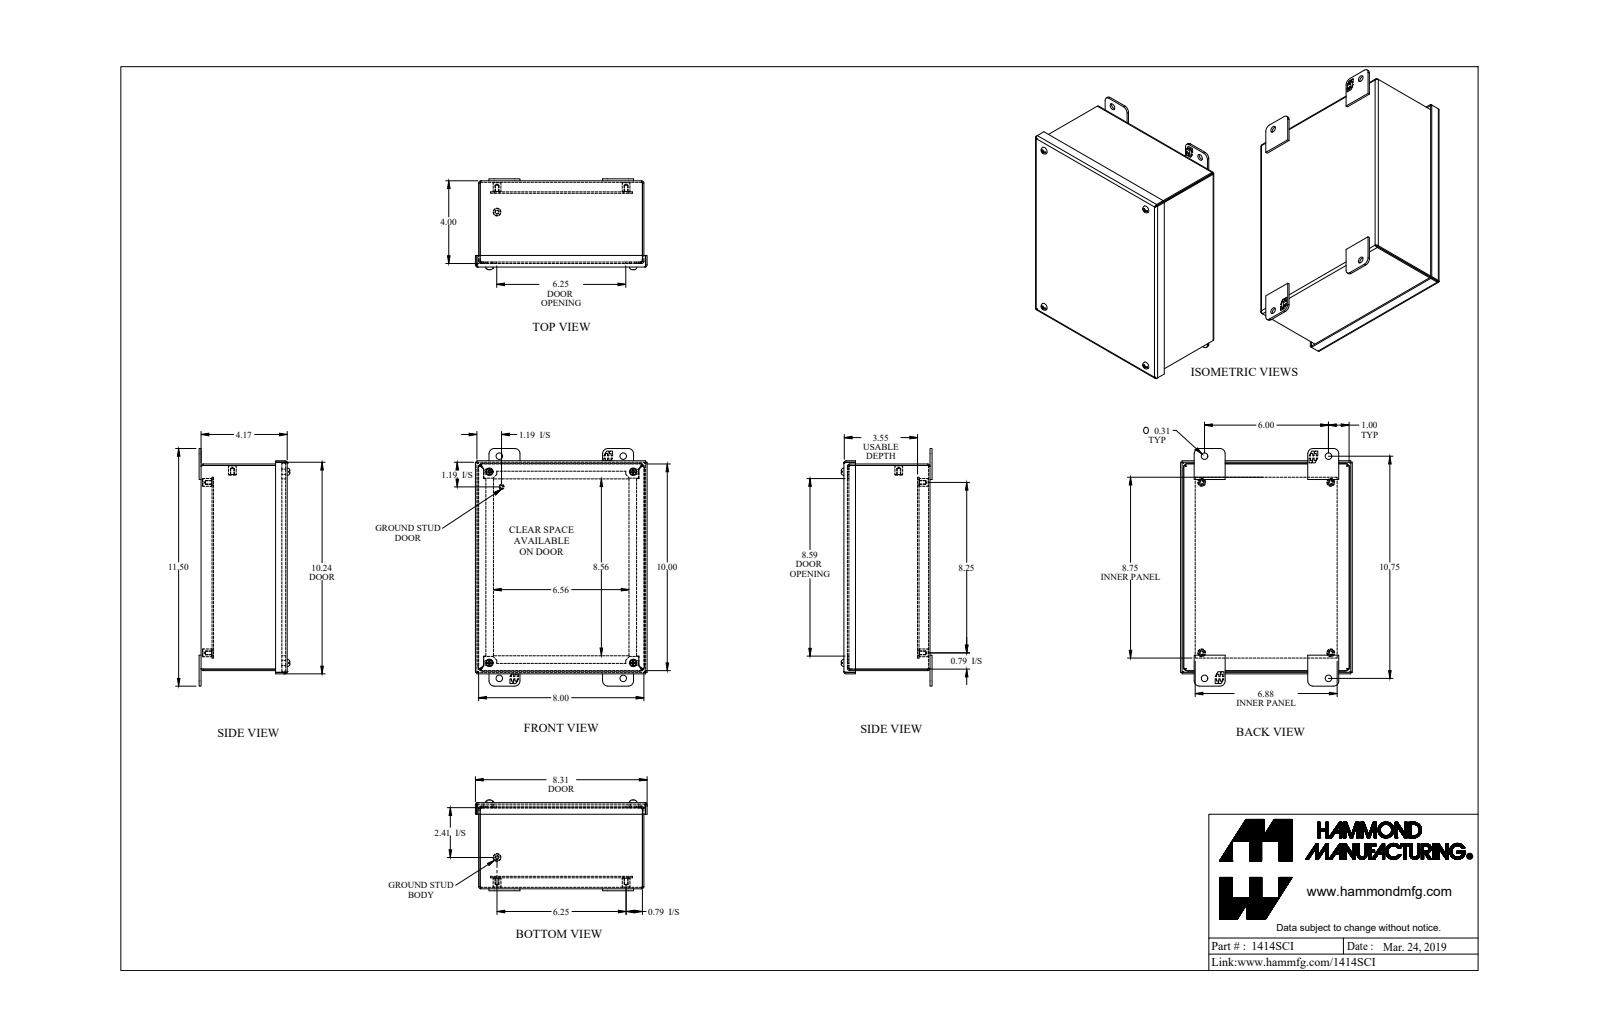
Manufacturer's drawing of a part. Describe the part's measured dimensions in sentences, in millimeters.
The part is named "1414SCI". Its 3-D file was written by "SolidWorks 2019 (AUTOMOTIVE_DESIGN)". It is 26 solids with 638 faces: 442 planar, 136 cylindrical and 60 other. Overall it measures 292.1 by 211.1 by 111.6 millimeters. Its volume is 555 700 cubic millimeters and its surface area 571 200 square millimeters. Round holes: 5 of diameter 4, 4 of diameter 4, 4 of diameter 6.7, 4 of diameter 7.9. Round bosses or shafts: 5 of diameter 9.5, 4 of diameter 9.9, 4 of diameter 7, 4 of diameter 4.8, 4 of diameter 3.8, 1 of diameter 6.4, 1 of diameter 4.8. Partial cylindrical surfaces (rounded edges, fillets, slot ends): 12 of radius 3.2, 12 of radius 6.4, 8 of radius 0.9, 8 of radius 1.2, 8 of radius 2.7, 8 of radius 3, 8 of radius 7.1, 4 of radius 4.1. The main face-to-face distances are 1.8, 104.1, 90.6, 13.5, 106, 102.3, 201.4, 92.5, 11.7, 88.8. The hole center spacings are 152.4, 158.8, 176.7, 209.6, 235, 254.2, 254.4, 262.9.
